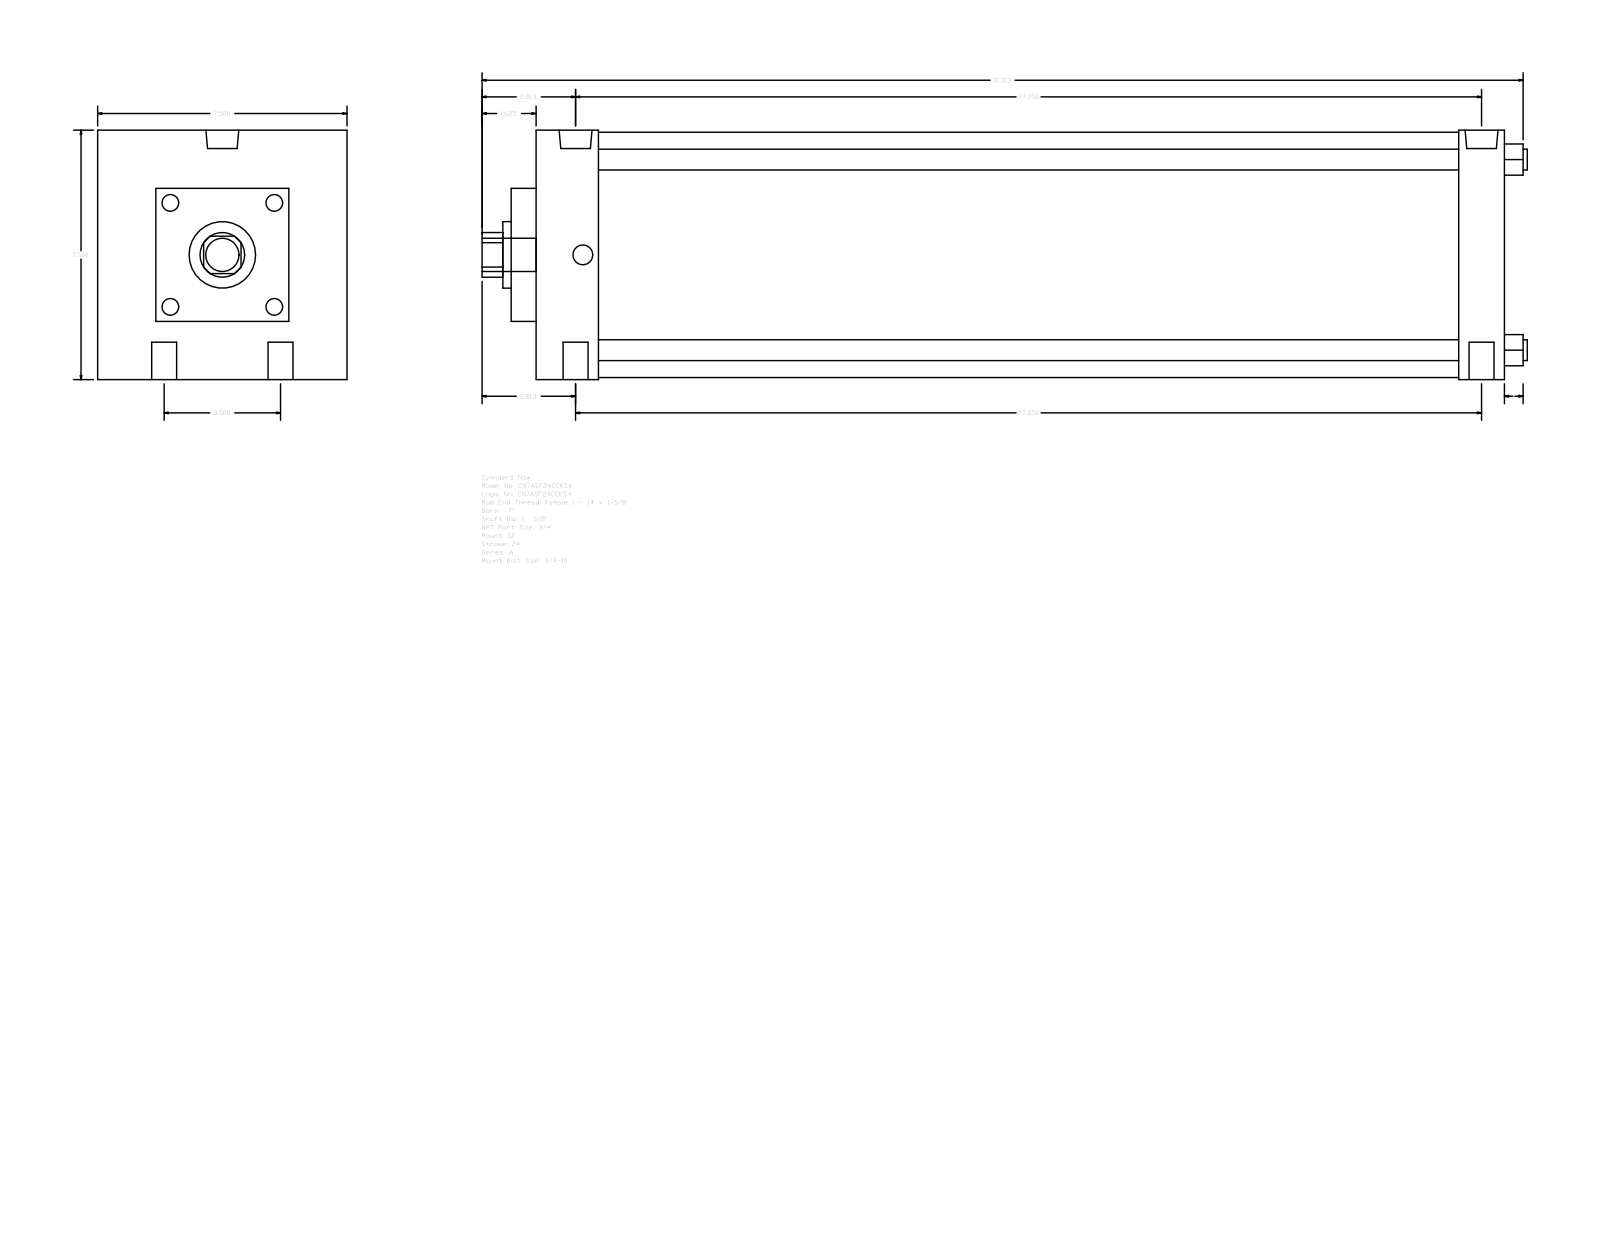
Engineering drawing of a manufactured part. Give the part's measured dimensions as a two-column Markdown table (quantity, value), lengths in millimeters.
| quantity | value |
| --- | --- |
| part name | A_SF__0700_1.375 |
| STEP written by | GSSL Pune (CONFIG_CONTROL_DESIGN) |
| units | millimeters |
| bodies | 0 solids, 93 faces (67 planar, 26 cylindrical, 0 other) |
| overall size | 798.51 × 190.5 × 190.5 |
| round holes (diameter × count) | 19.05 × 4, 15.08 × 2, 25.12 × 2, 34.92 × 1, 50.8 × 1 |
| round bosses / shafts (diameter × count) | 15.88 × 4, 187.32 × 1, 25.4 × 1 |
| partial cylindrical surfaces (radius × count) | 17.06 × 1 |
| main face-to-face distances | 190.5, 739.78, 19.04, 758.82, 66.67, 723.89, 47.63, 704.85, 657.22, 692.15 |
| hole center spacings | 44.45, 693.58, 692.15, 88.9, 697.84, 681.03 |
